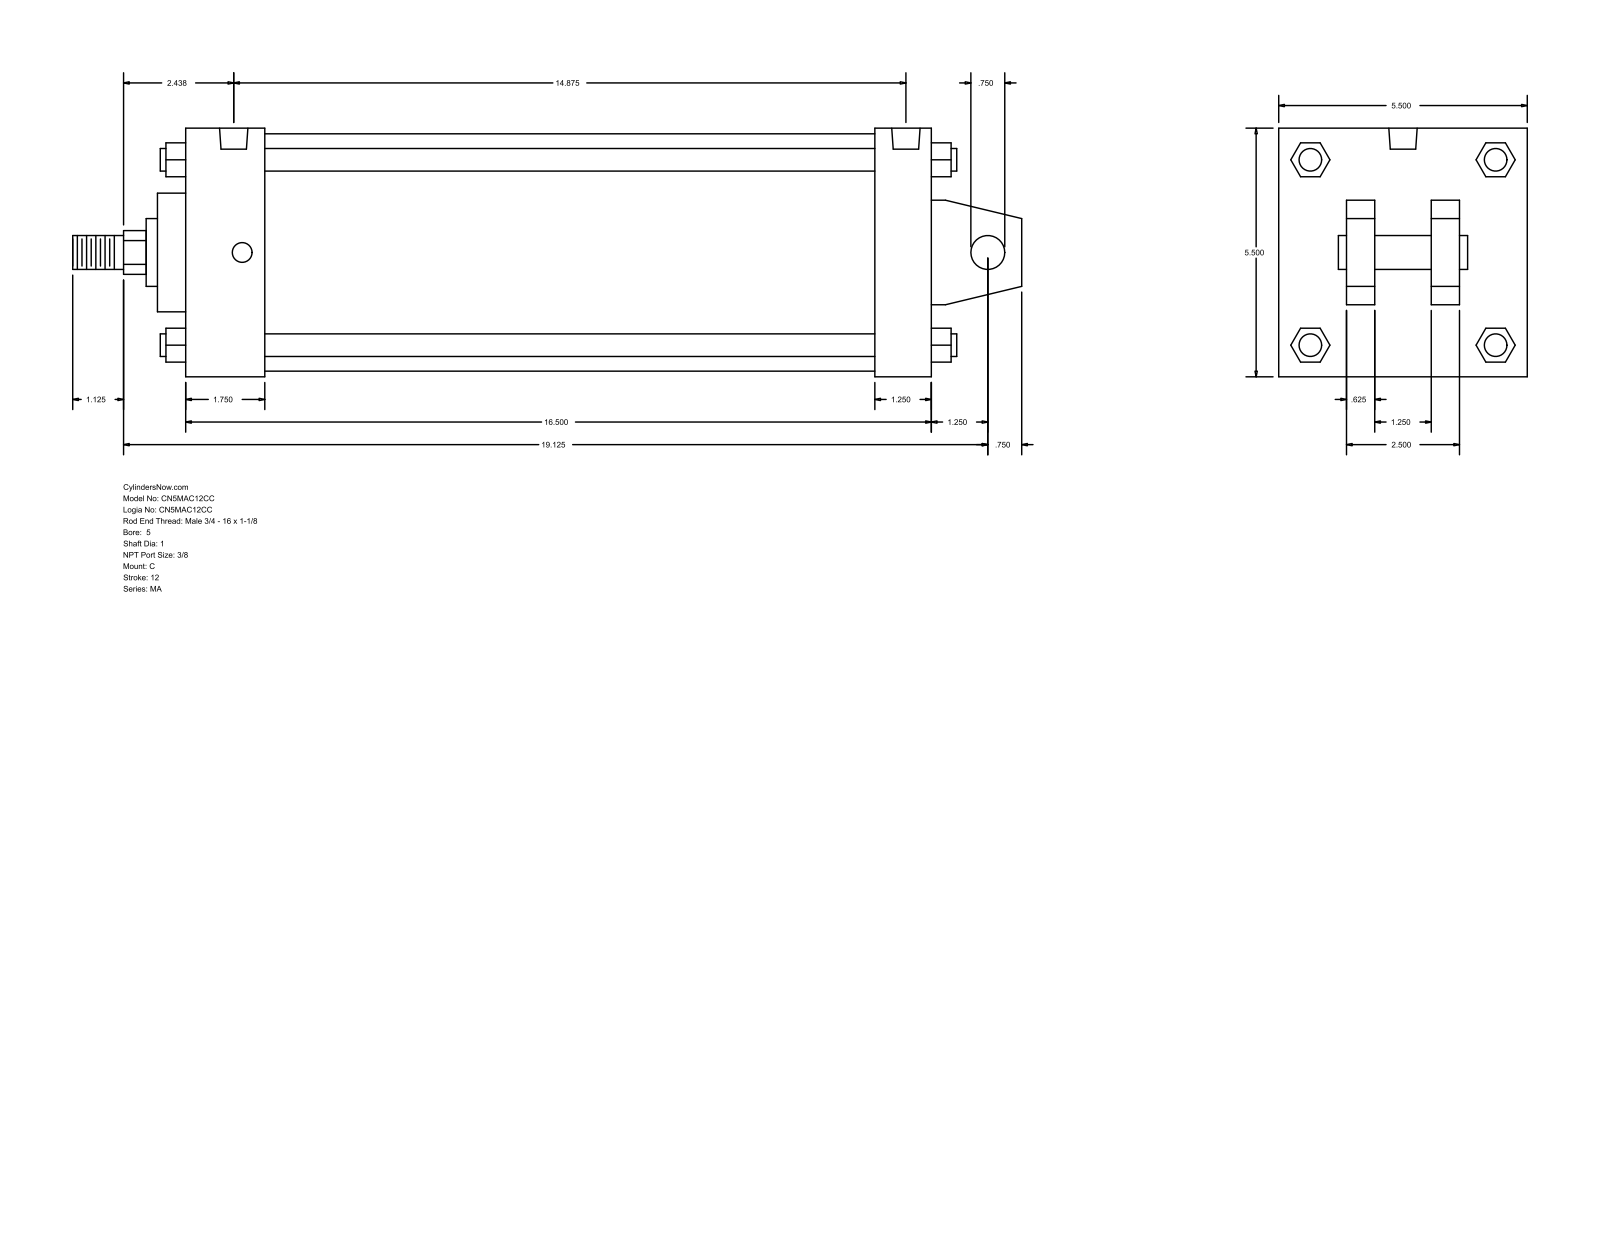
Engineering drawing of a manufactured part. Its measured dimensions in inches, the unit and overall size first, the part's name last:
Units: inches
Overall size (bounding box): 21 × 5.5 × 5.5
Round holes (diameter × count): ⌀0.437 ×4, ⌀0.627 ×2
Round bosses / shafts (diameter × count): ⌀0.5 ×4, ⌀0.75 ×2, ⌀5.25 ×1, ⌀2.625 ×1, ⌀1.5 ×1, ⌀1 ×1
Partial cylindrical surfaces — rounded edges, fillets, slot ends (radius × count): R0.484 ×1
Main face-to-face distances: 5.5, 16.5, 0.625, 15.25, 1.25, 1.75, 13.5, 14.75, 1.5, 4
Hole centre spacings: 0.187, 14.5, 14.688, 14.875
Bodies: 0 solids, 141 faces (109 planar, 32 cylindrical, 0 other)
Part name (STEP PRODUCT): MA_C__0500_1
STEP written by: GSSL Pune (CONFIG_CONTROL_DESIGN)
